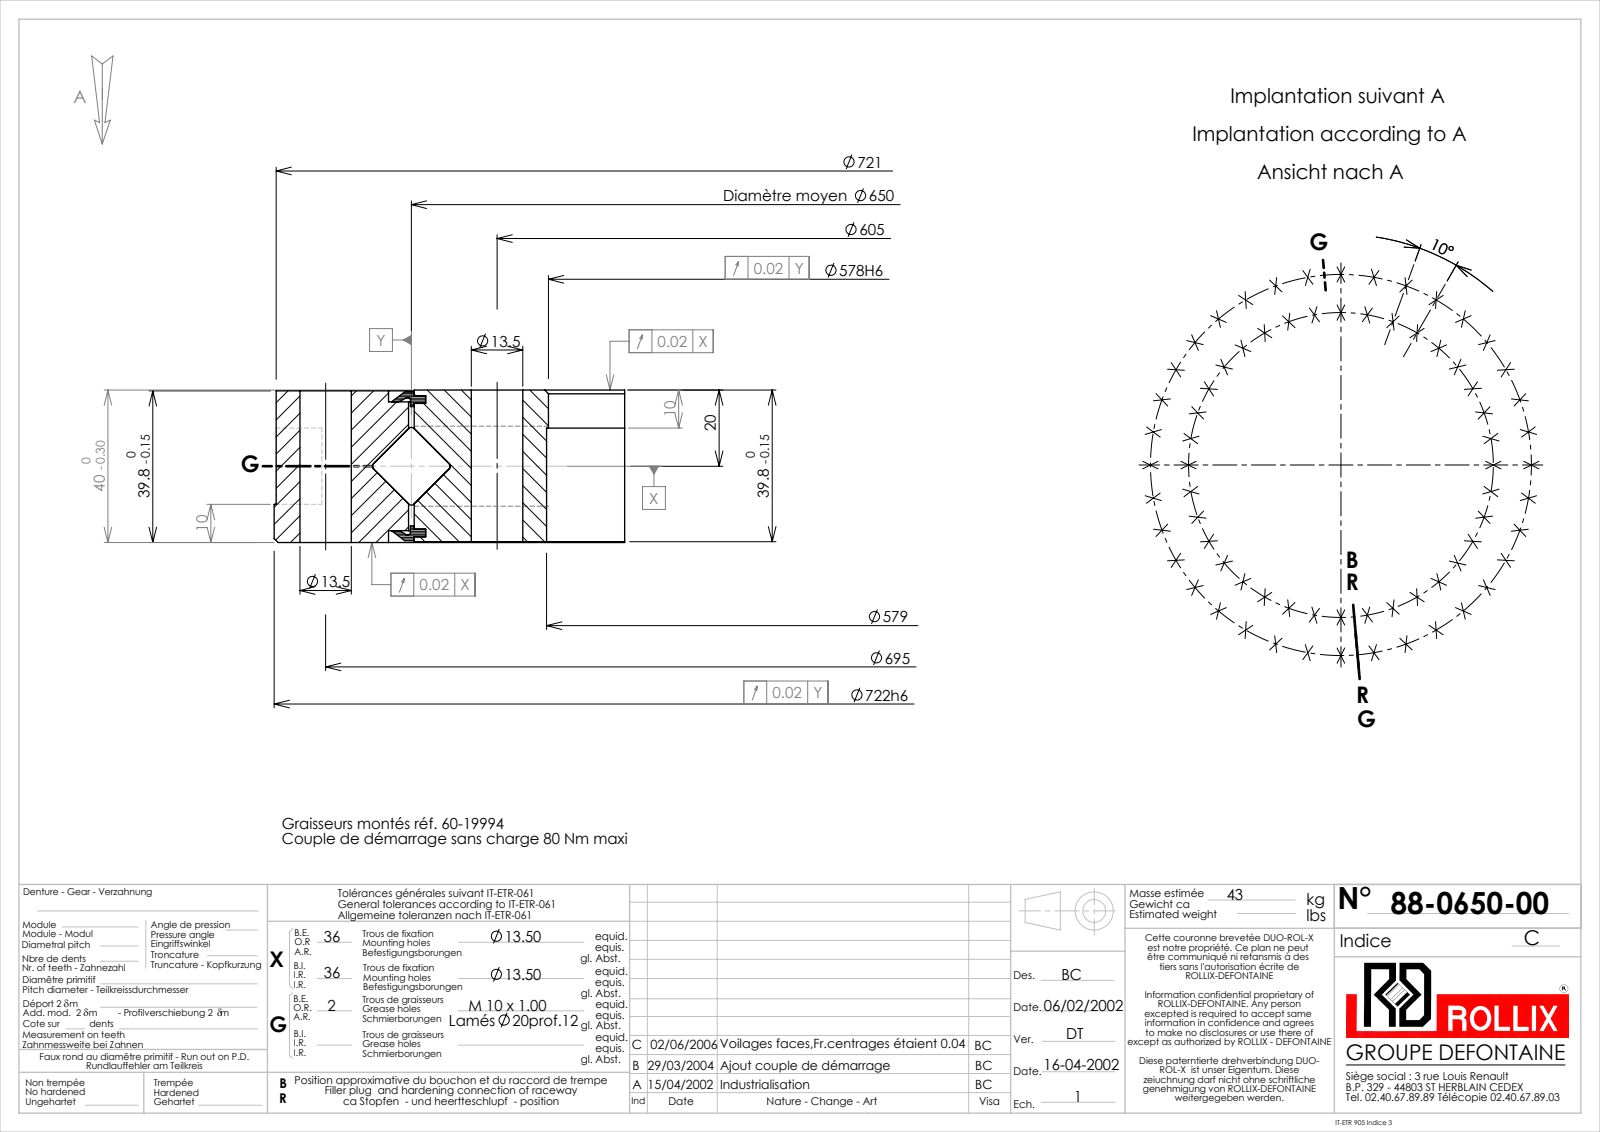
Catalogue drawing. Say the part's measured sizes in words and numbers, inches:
The part is named "88-0650-00". Its 3-D file was written by "SolidWorks 2016 (CONFIG_CONTROL_DESIGN)". It is 7 solids with 303 faces: 46 planar, 202 cylindrical and 55 other. Overall it measures 28.425 by 28.425 by 1.575 inches. Its volume is 294.9 cubic inches and its surface area 1 355 square inches. Round holes: 72 of diameter 0.531, 2 of diameter 0.354, 2 of diameter 0.787, 1 of diameter 22.756, 1 of diameter 22.795, 1 of diameter 25.295, 1 of diameter 25.531, 1 of diameter 25.65, 1 of diameter 26.063. Round bosses or shafts: 2 of diameter 0.394, 1 of diameter 28.425, 1 of diameter 28.386, 1 of diameter 25.61, 1 of diameter 0.591. The main face-to-face distances are 1.567, 1.559, 1.575, 0.122, 1.453, 0.114, 1.445, 0.138, 1.437, 0.13. The hole center spacings are 11.564, 13.681, 20.961, 22.414, 24.798, 26.946, 2.385, 27.258.
